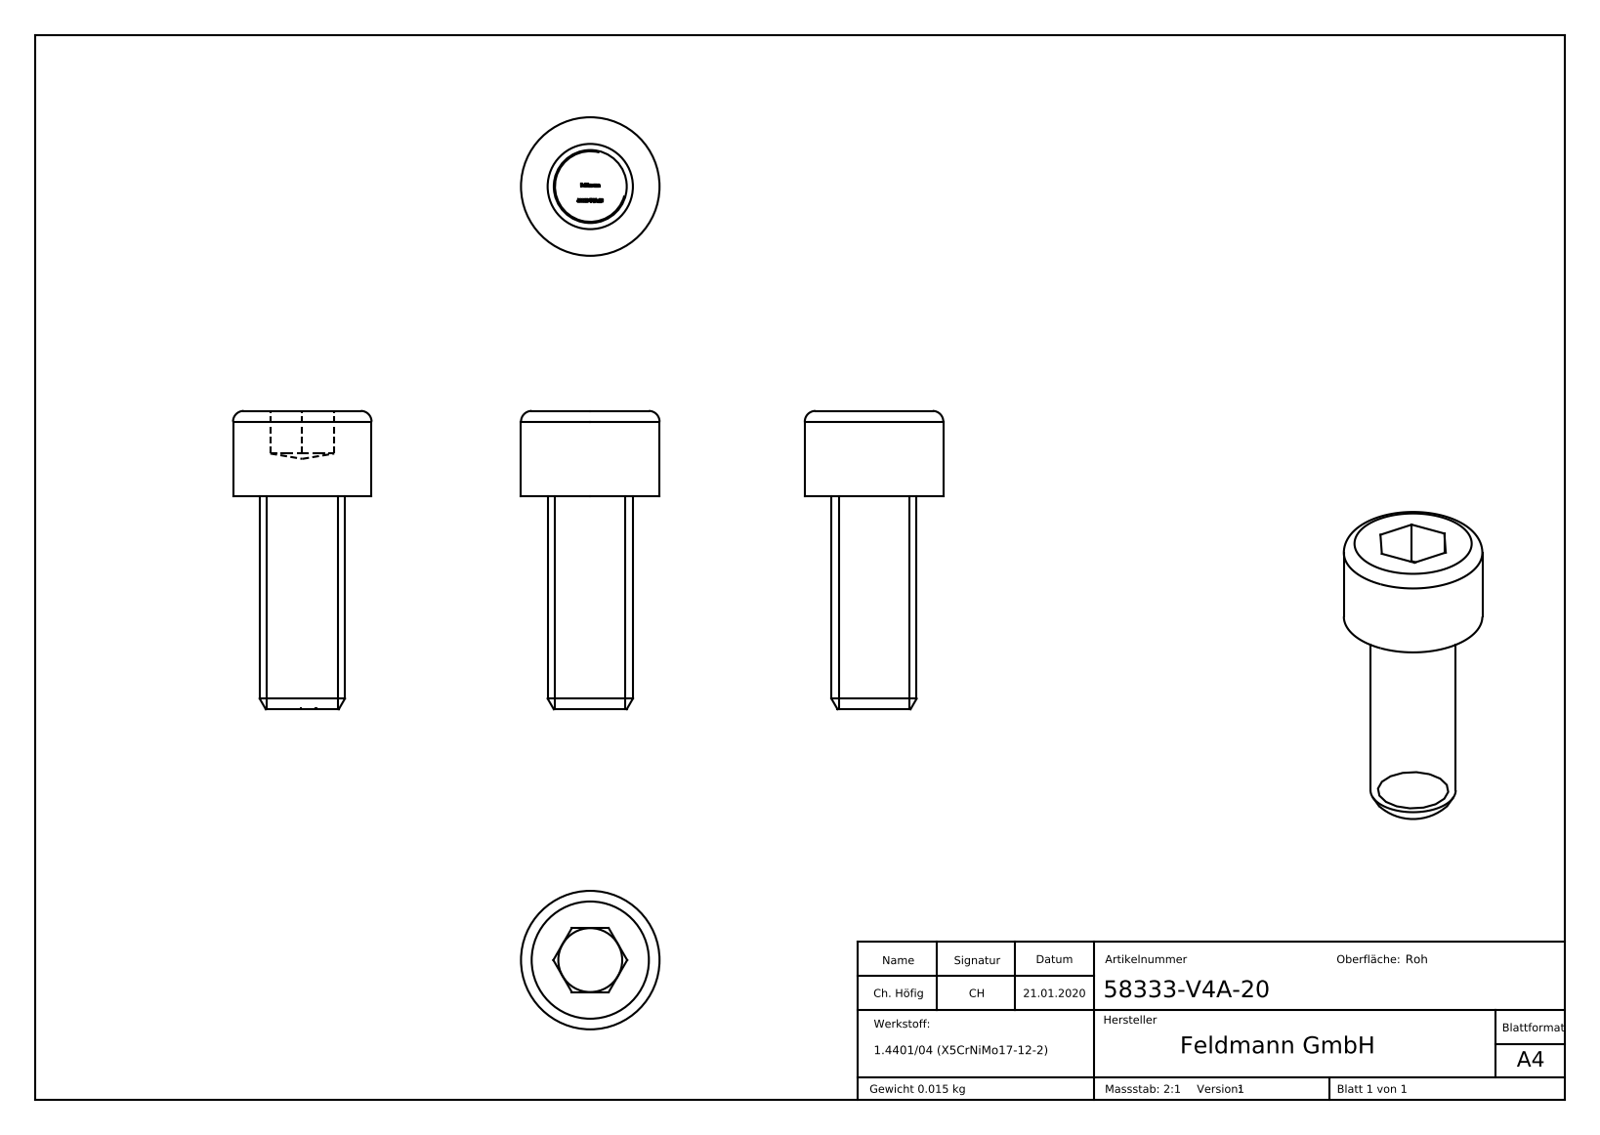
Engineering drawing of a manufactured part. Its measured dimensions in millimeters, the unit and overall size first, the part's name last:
Units: millimetres
Overall size (bounding box): 29 × 13 × 13
Round bosses / shafts (diameter × count): ⌀13 ×1, ⌀8 ×1
Main face-to-face distances: 8, 6, 20, 28, 4, 24, 19.9, 23.9, 27.9, 1.44
Volume: 1 922 mm³ · Surface area: 1 151 mm²
Bodies: 1 solid, 292 faces (157 planar, 2 cylindrical, 133 other)
Part name (STEP PRODUCT): 58333-V4A-20
STEP written by: SolidWorks 2015 (CONFIG_CONTROL_DESIGN)
